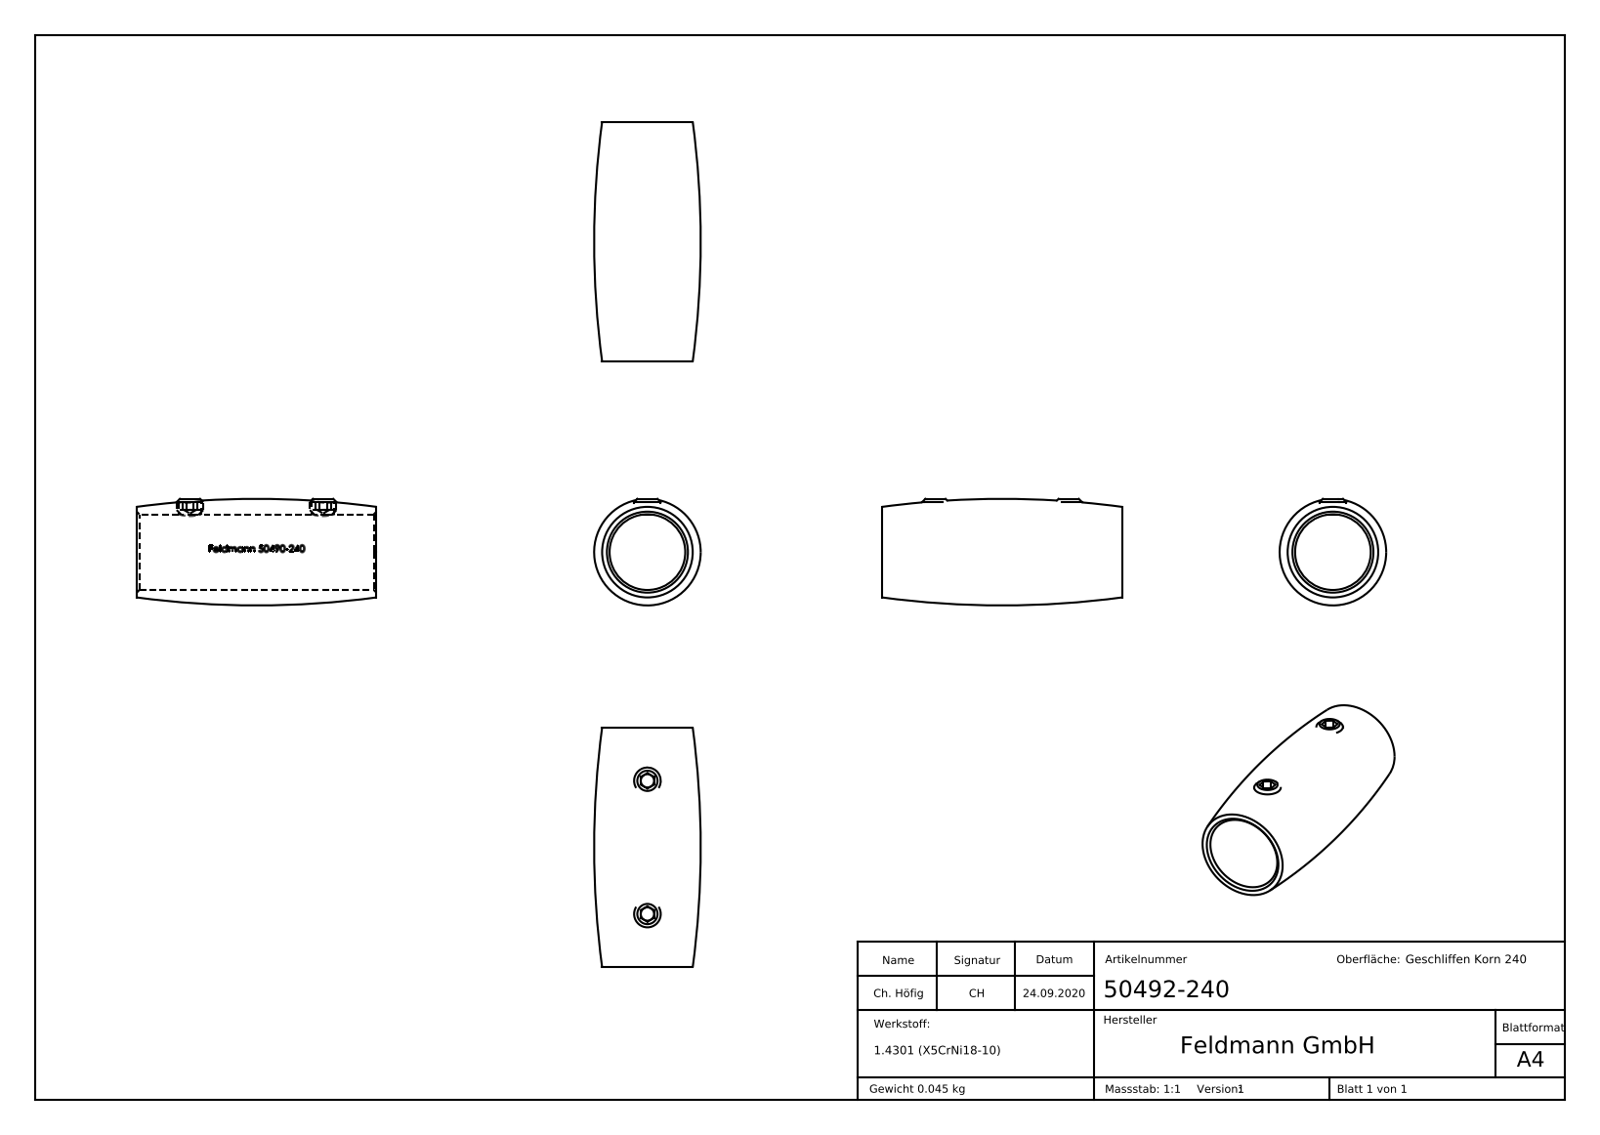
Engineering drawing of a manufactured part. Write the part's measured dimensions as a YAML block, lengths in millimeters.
part_name: "50492-240; DIN913_DIN 913 M5x3; 5049X-240 Teil1_50492-240 Teil1"
step_written_by: "SolidWorks 2018 (CONFIG_CONTROL_DESIGN)"
units: millimeters
bodies: {solids: 3, faces: 267, planar: 129, cylindrical: 31, other: 107}
overall_size: [45, 20, 20]
volume: 5660
surface_area: 5011
round_holes:
  - {diameter: 4.2, count: 2}
  - {diameter: 14.2, count: 1}
round_bosses_or_shafts:
  - {diameter: 5, count: 2}
partial_cylinders:
  - {radius: 7.2, count: 1}
face_to_face_distances: [45, 3, 21.65, 2.49, 24.14, 19.16, 2.5, 1, 2, 8.68]
hole_center_spacings: [25]
